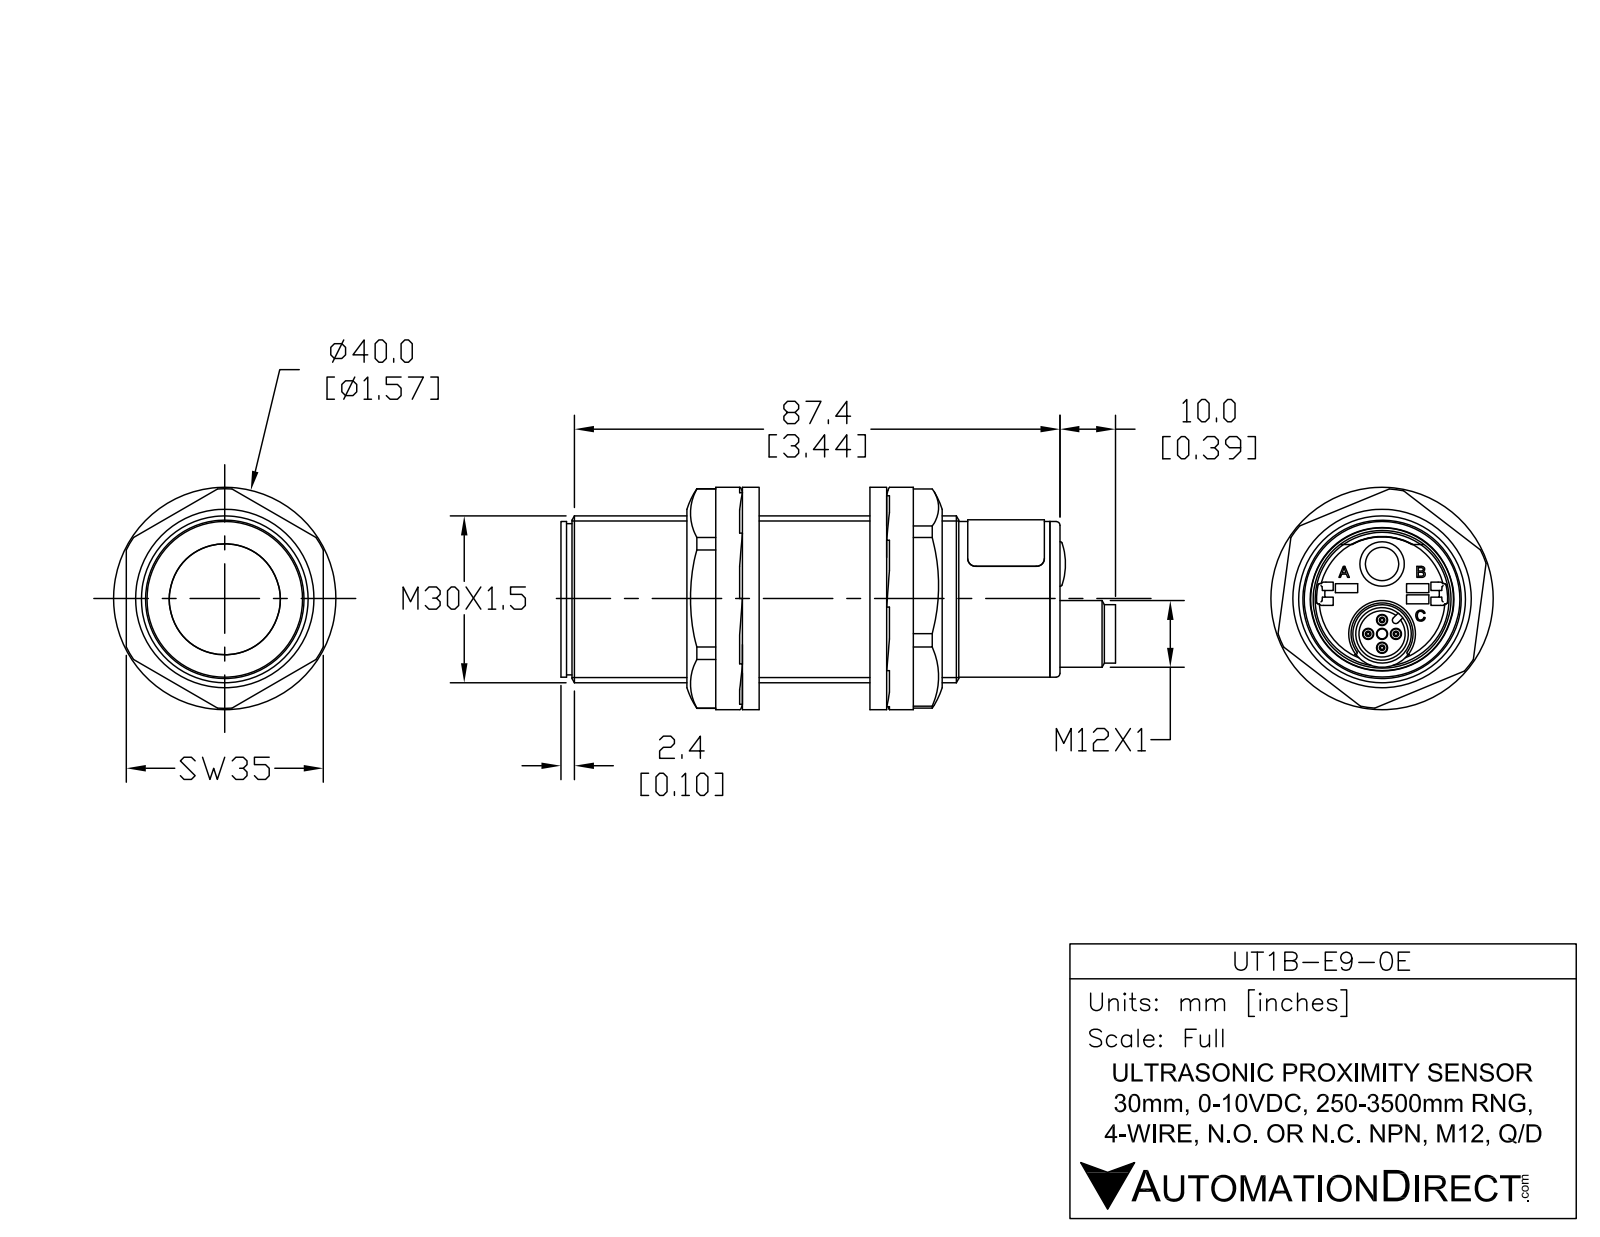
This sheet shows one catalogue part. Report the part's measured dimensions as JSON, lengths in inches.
{"part_name": "UT1B-E9-0E", "step_written_by": "SolidWorks 2017 (AUTOMOTIVE_DESIGN)", "units": "inches", "bodies": {"solids": 5, "faces": 107, "planar": 30, "cylindrical": 45, "other": 32}, "overall_size": [3.89, 1.181, 1.181], "volume_in3": 3.754, "surface_area_in2": 20.71, "round_holes": [[0.071, 4], [0.315, 1], [0.327, 1], [0.372, 1], [0.925, 1]], "round_bosses_or_shafts": [[0.039, 4], [1.181, 1], [1.102, 1], [1.071, 1], [0.472, 1], [0.413, 1], [0.364, 1]], "partial_cylinders_radius": [[0.012, 2], [0.024, 1]], "face_to_face_distances": [3.386, 3.457, 0.039, 3.425, 0.071, 3.496, 0.039, 0.059, 3.425, 3.496], "hole_center_spacings": [0.098, 0.139, 0.197, 0.264, 0.505, 0.146, 0.245, 0.25]}
